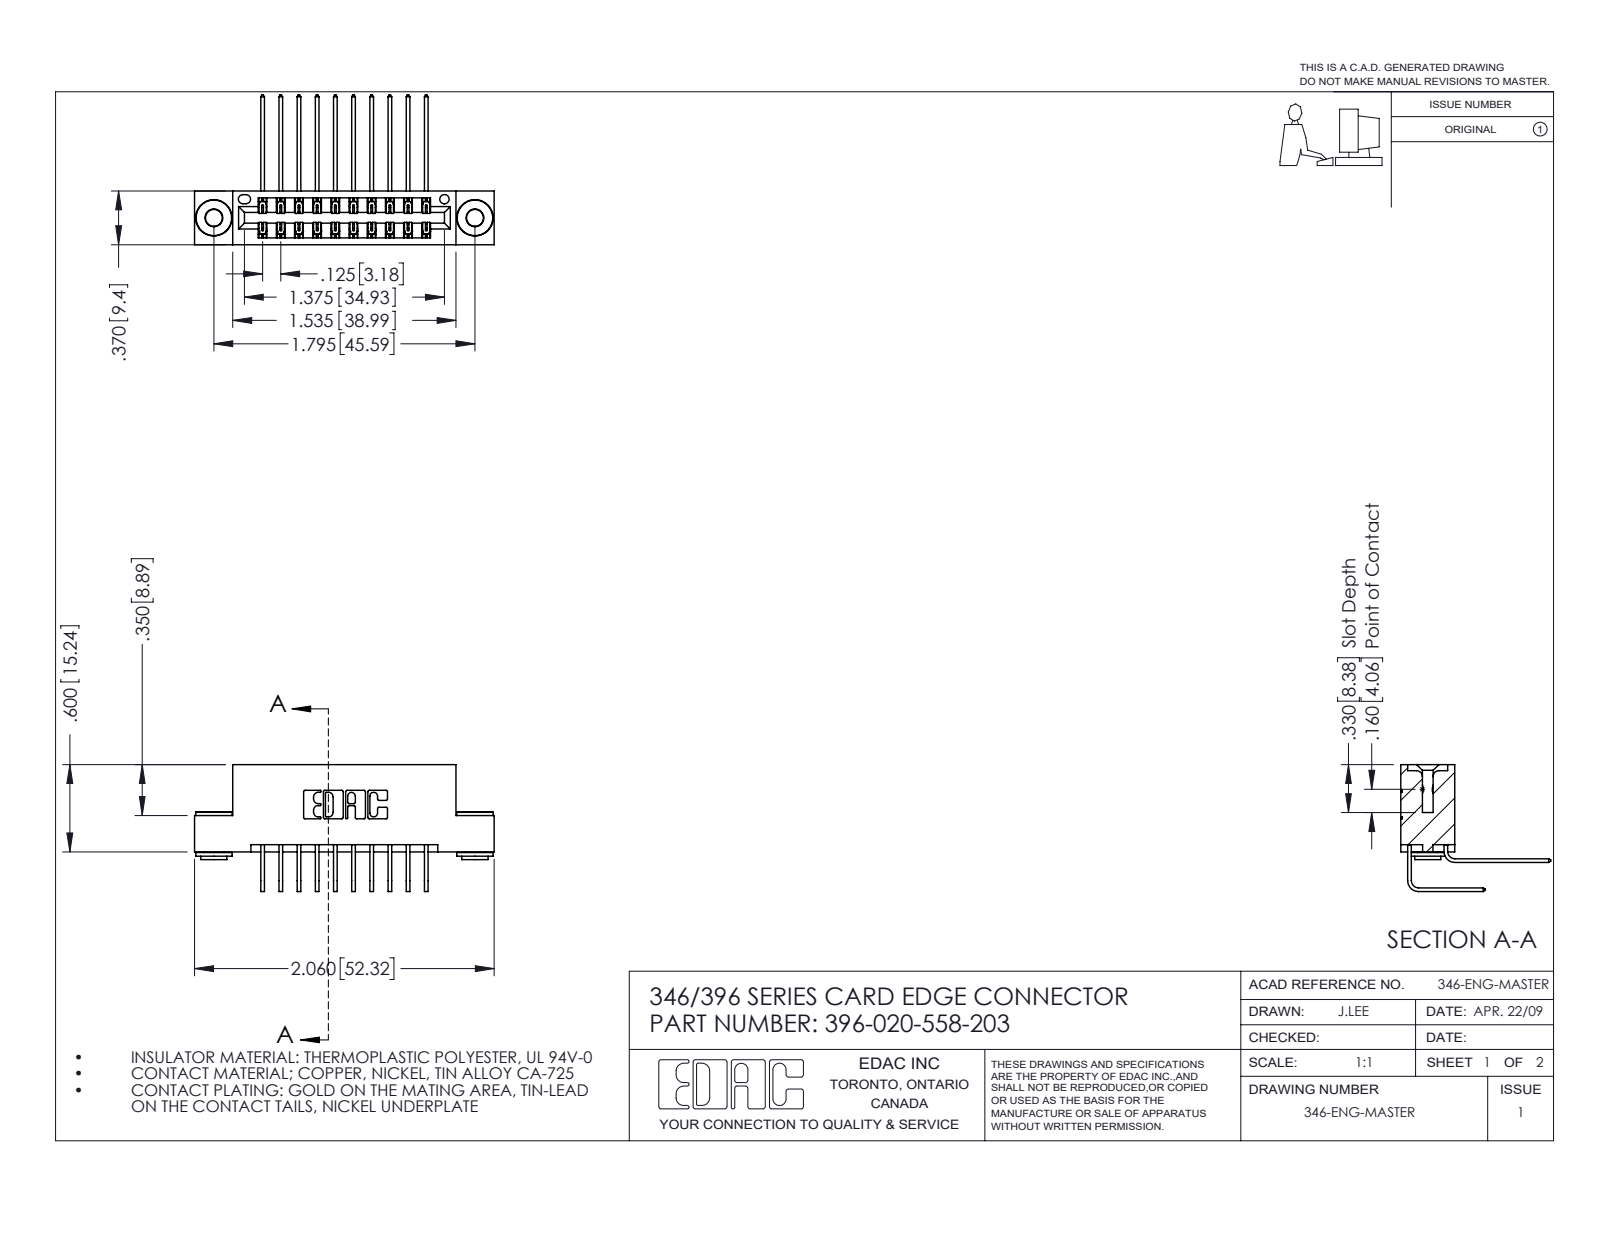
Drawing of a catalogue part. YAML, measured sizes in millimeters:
part_name: "345-292-001_558 559 Tail - 1; 396-020-558-203; 346 Part_Flush Mounting Lugs - 0.156 Dia-TH; 345-250-002_345-250-002-102 (+1 more)"
step_written_by: "SolidWorks 2016 (CONFIG_CONTROL_DESIGN)"
units: millimeters
bodies: {solids: 23, faces: 1240, planar: 826, cylindrical: 406, other: 8}
overall_size: [52.3, 26.2, 22.2]
volume: 4980
surface_area: 7123
round_holes:
  - {diameter: 2.9, count: 2}
  - {diameter: 4, count: 2}
  - {diameter: 1.6, count: 1}
round_bosses_or_shafts:
  - {diameter: 6.4, count: 2}
  - {diameter: 4.6, count: 2}
  - {diameter: 3.5, count: 2}
partial_cylinders:
  - {radius: 0.2, count: 30}
  - {radius: 0.3, count: 22}
  - {radius: 0.2, count: 6}
  - {radius: 0.8, count: 6}
  - {radius: 0.7, count: 3}
  - {radius: 0.4, count: 2}
  - {radius: 0.6, count: 2}
  - {radius: 0.6, count: 2}
face_to_face_distances: [6.4, 8.2, 1.2, 9.4, 0.6, 7.6, 1.8, 7, 3.8, 5.6]
hole_center_spacings: [6.2, 40.4, 45.6]
